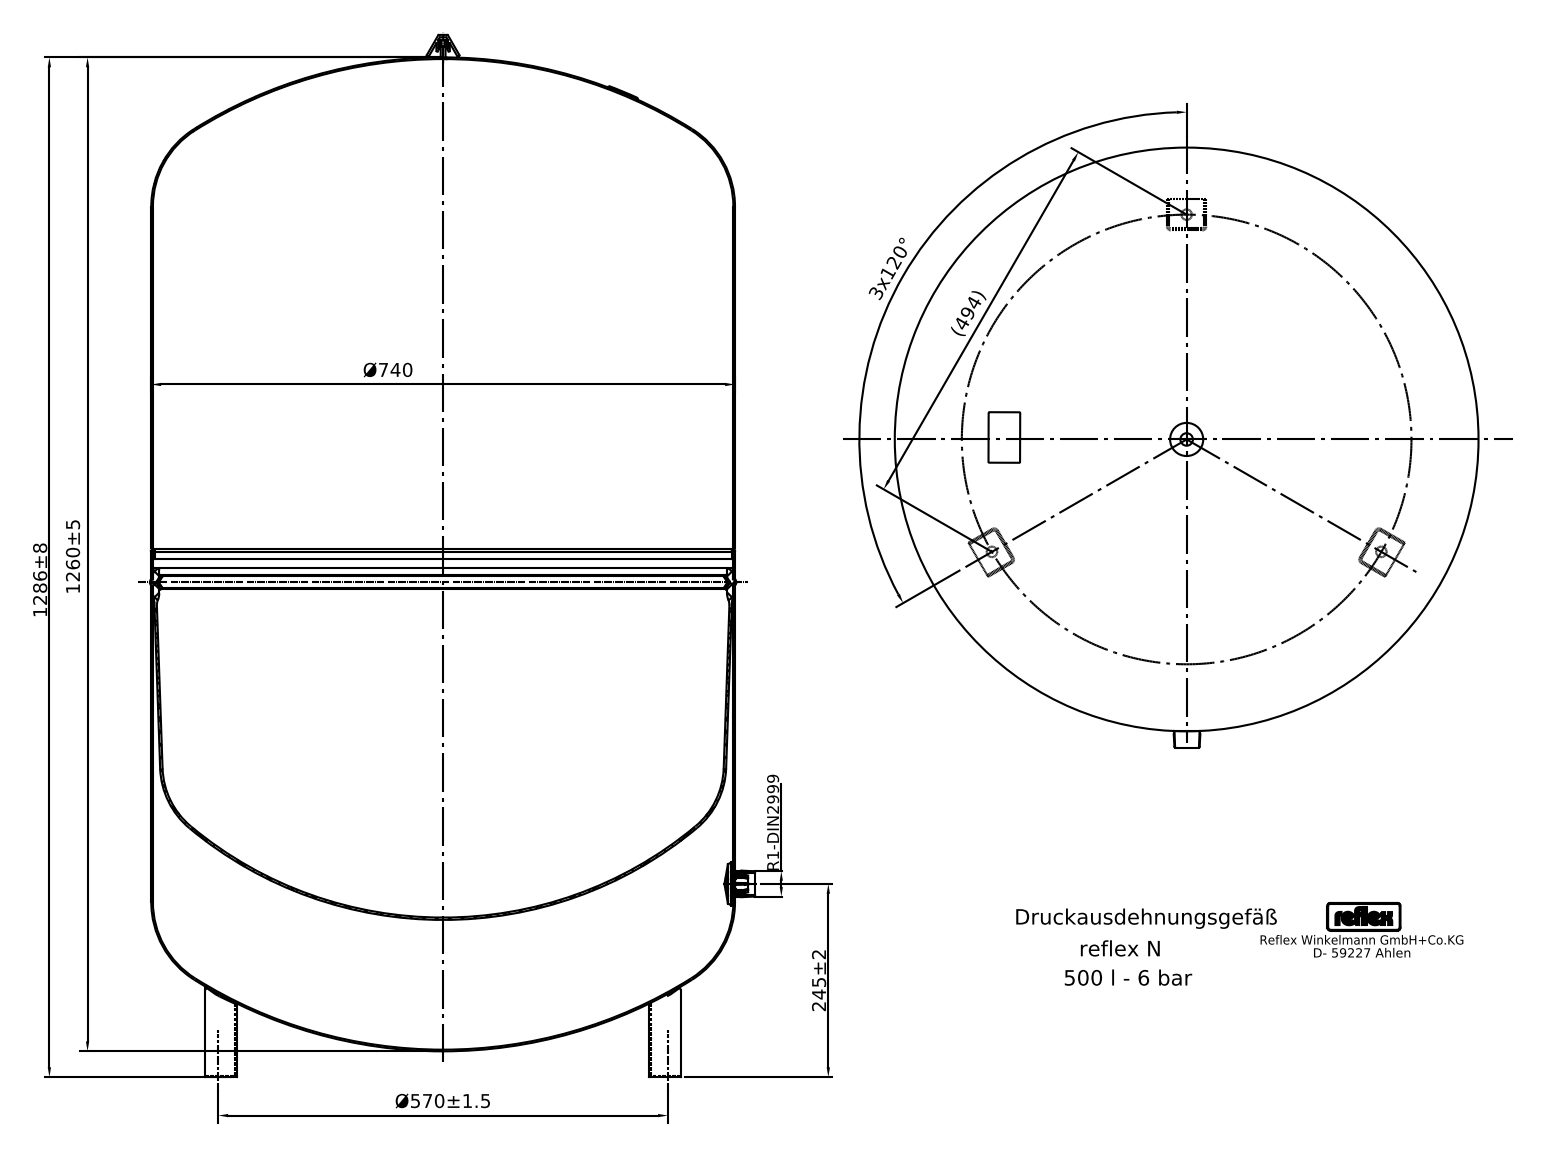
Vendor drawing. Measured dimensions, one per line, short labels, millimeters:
written by: Mechanical Desktop 2008 (CONFIG_CONTROL_DESIGN)
unit: mm
bodies: 16 solids, 250 faces (100 planar, 93 cylindrical, 57 other)
size: 1307.25 × 770.45 × 750.9
volume: 486 300 000 mm³; area: 5 104 000 mm²
holes: 3× ⌀13.4, 1× ⌀8.46, 1× ⌀25.7
bosses: 1× ⌀740, 1× ⌀33.7, 1× ⌀10.26, 1× ⌀5.4, 1× ⌀3.6
rounds: 15× R1, 15× R2.5, 15× R5, 4× R3.94, 3× R1.57, 2× R2.69, 2× R4.72, 2× R6.49
face distances: 882, 2.5, 47.5, 45, 50, 441, 660, 217, 658, 1099
hole spacings: 285, 493.64
